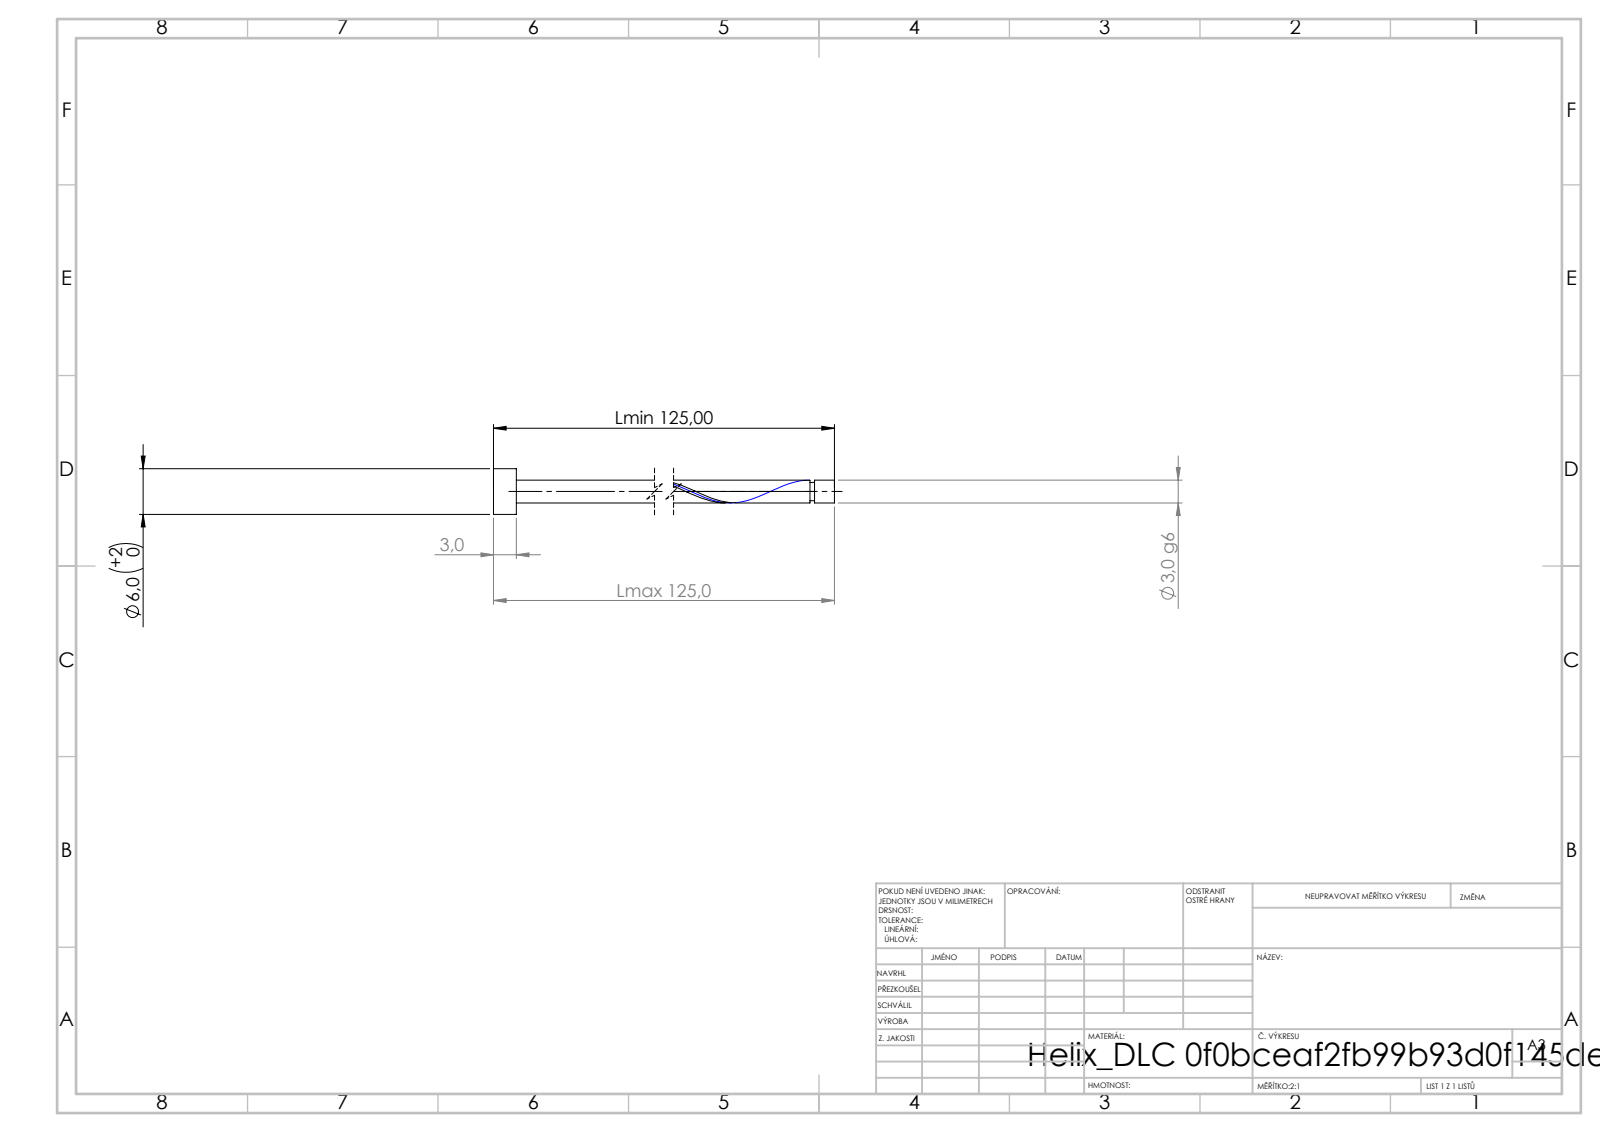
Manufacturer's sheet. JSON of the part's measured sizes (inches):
{"step_written_by": "SolidWorks 2019 (CONFIG_CONTROL_DESIGN)", "units": "inches", "bodies": {"solids": 1, "faces": 21, "planar": 6, "cylindrical": 14, "other": 1}, "overall_size": [4.921, 0.236, 0.236], "volume_in3": 0.057, "surface_area_in2": 1.995, "round_bosses_or_shafts": [[0.236, 1], [0.118, 1], [0.094, 1]], "face_to_face_distances": [0.118, 4.921, 4.803, 4.818, 4.7, 0.103, 4.794, 4.676, 0.024, 0.127]}
